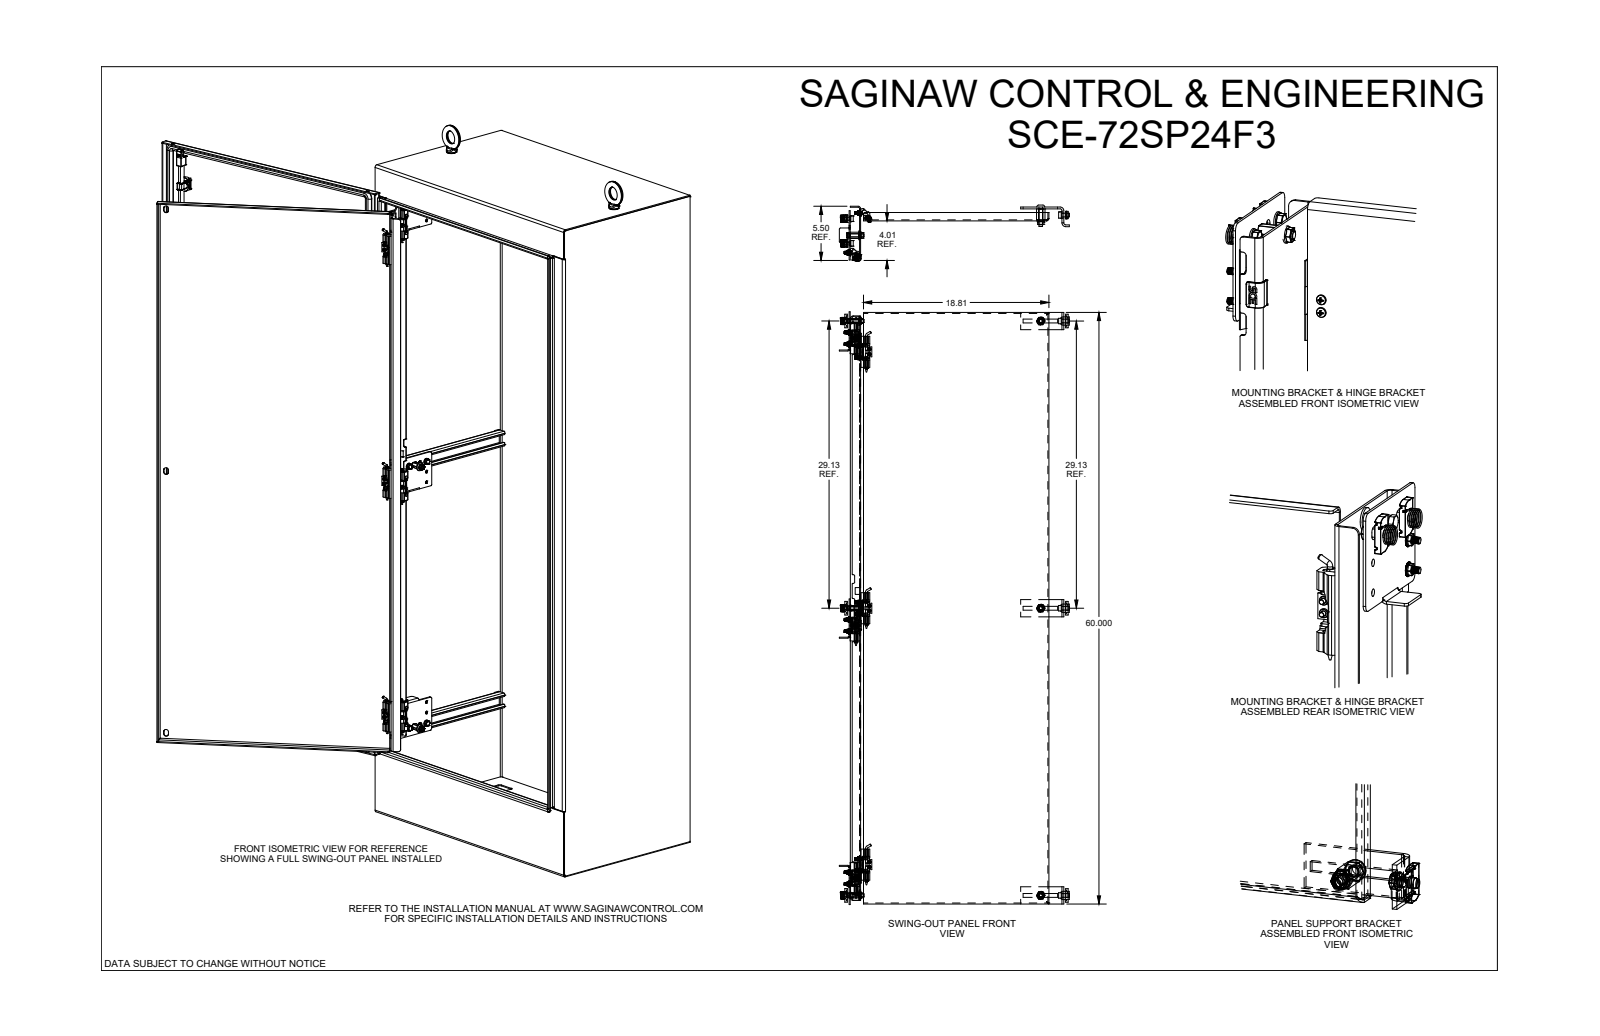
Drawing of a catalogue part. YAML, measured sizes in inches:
part_name: "SCE-72SP24F3"
step_written_by: "SolidWorks 2021 (AUTOMOTIVE_DESIGN)"
units: inches
bodies: {solids: 53, faces: 2490, planar: 1213, cylindrical: 926, other: 351}
overall_size: [60.119, 23.336, 5.681]
volume: 190.8
surface_area: 3632
round_holes:
  - {diameter: 0.25, count: 18}
  - {diameter: 0.281, count: 18}
  - {diameter: 0.36, count: 12}
  - {diameter: 0.218, count: 9}
  - {diameter: 0.04, count: 6}
  - {diameter: 0.19, count: 6}
  - {diameter: 0.156, count: 3}
  - {diameter: 0.201, count: 3}
  - {diameter: 0.33, count: 3}
  - {diameter: 0.383, count: 3}
  - {diameter: 0.375, count: 2}
  - {diameter: 0.204, count: 1}
round_bosses_or_shafts:
  - {diameter: 0.196, count: 8}
  - {diameter: 0.34, count: 6}
  - {diameter: 0.249, count: 6}
  - {diameter: 0.886, count: 3}
  - {diameter: 0.813, count: 3}
  - {diameter: 0.5, count: 3}
  - {diameter: 0.368, count: 3}
  - {diameter: 0.31, count: 3}
partial_cylinders:
  - {radius: 0.011, count: 54}
  - {radius: 0.188, count: 31}
  - {radius: 0.015, count: 28}
  - {radius: 0.25, count: 22}
  - {radius: 0.1, count: 18}
  - {radius: 0.06, count: 17}
  - {radius: 0.03, count: 16}
  - {radius: 0.13, count: 14}
face_to_face_distances: [0.104, 1.058, 1.385, 19.108, 20.166, 5.396, 4.011, 0.954, 1.162, 1.281]
hole_center_spacings: [0.592, 29.125, 26, 1.181, 25.625, 54.75, 2.098, 2.92]
